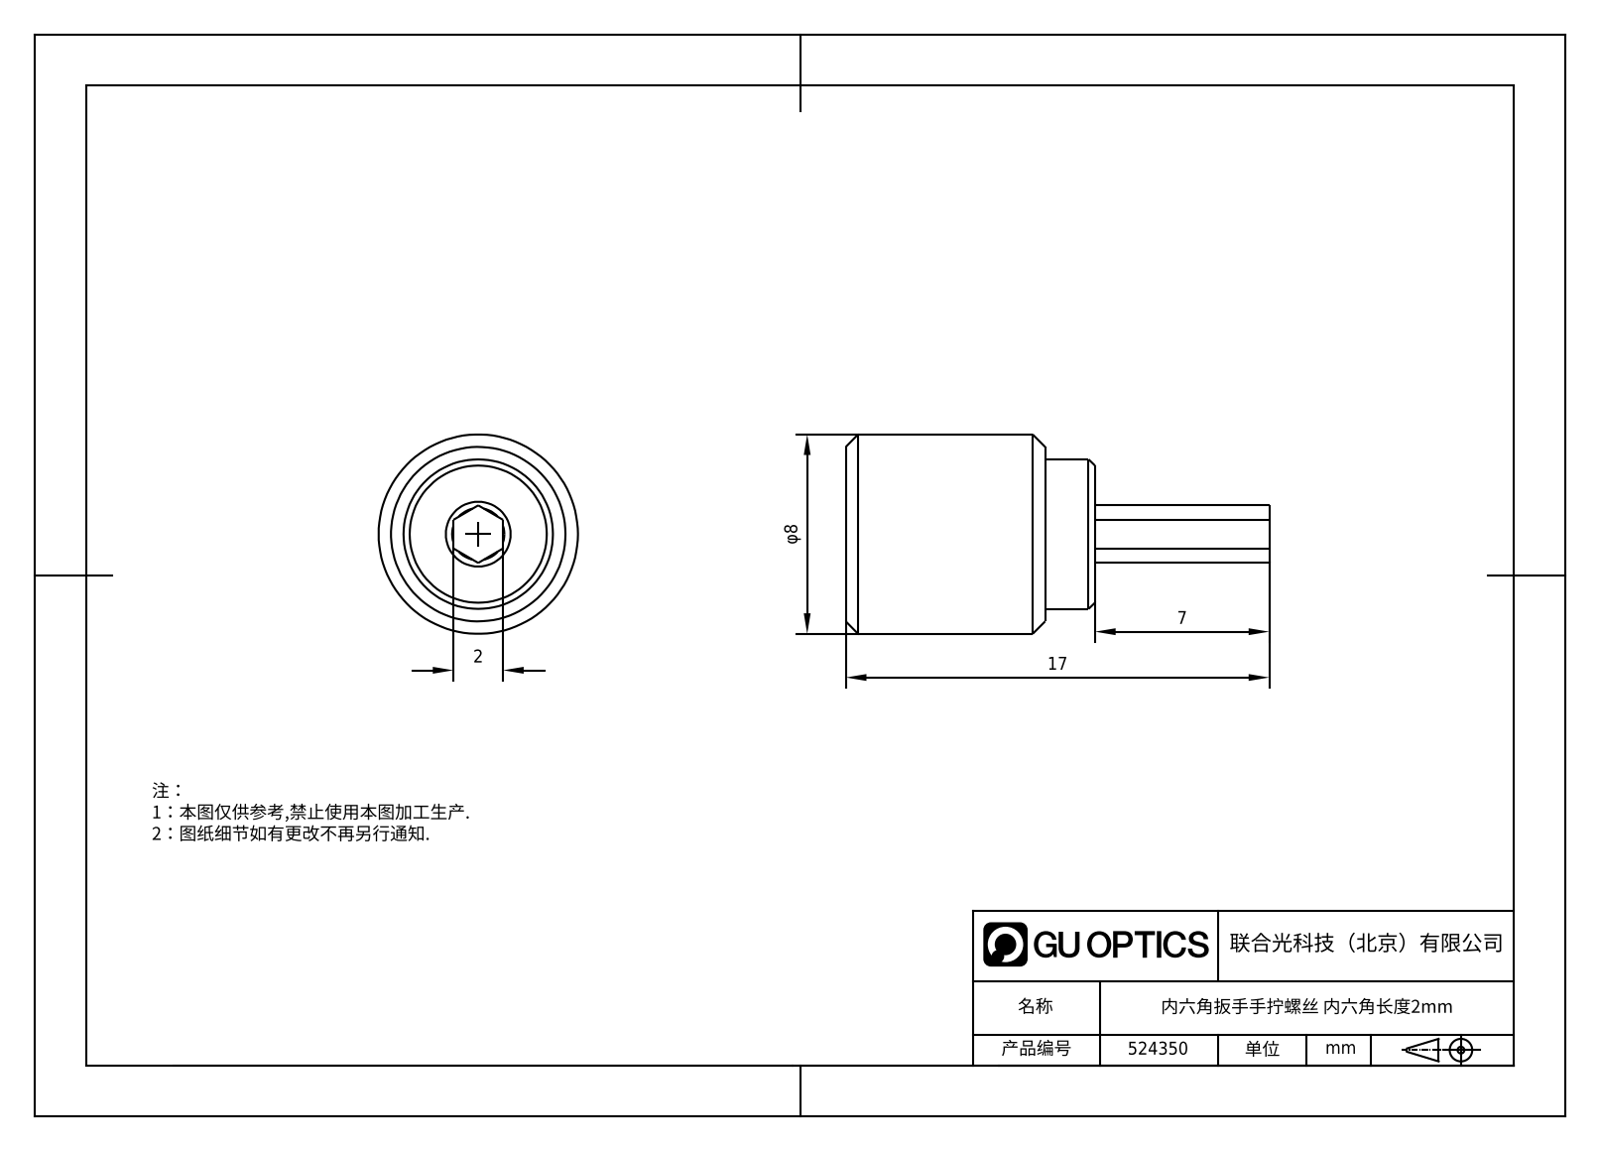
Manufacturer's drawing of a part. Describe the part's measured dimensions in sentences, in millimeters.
Its 3-D file was written by "SolidWorks 2021 (CONFIG_CONTROL_DESIGN)". It is 2 solids with 26 faces: 12 planar, 6 cylindrical and 8 other. Overall it measures 17 by 8 by 8 millimeters. Its volume is 476 cubic millimeters and its surface area 430 square millimeters. Round holes: 1 of diameter 2.1. Round bosses or shafts: 1 of diameter 8, 1 of diameter 6. The main face-to-face distances are 2, 10, 8, 6, 4, 17, 11, 9, 7.
